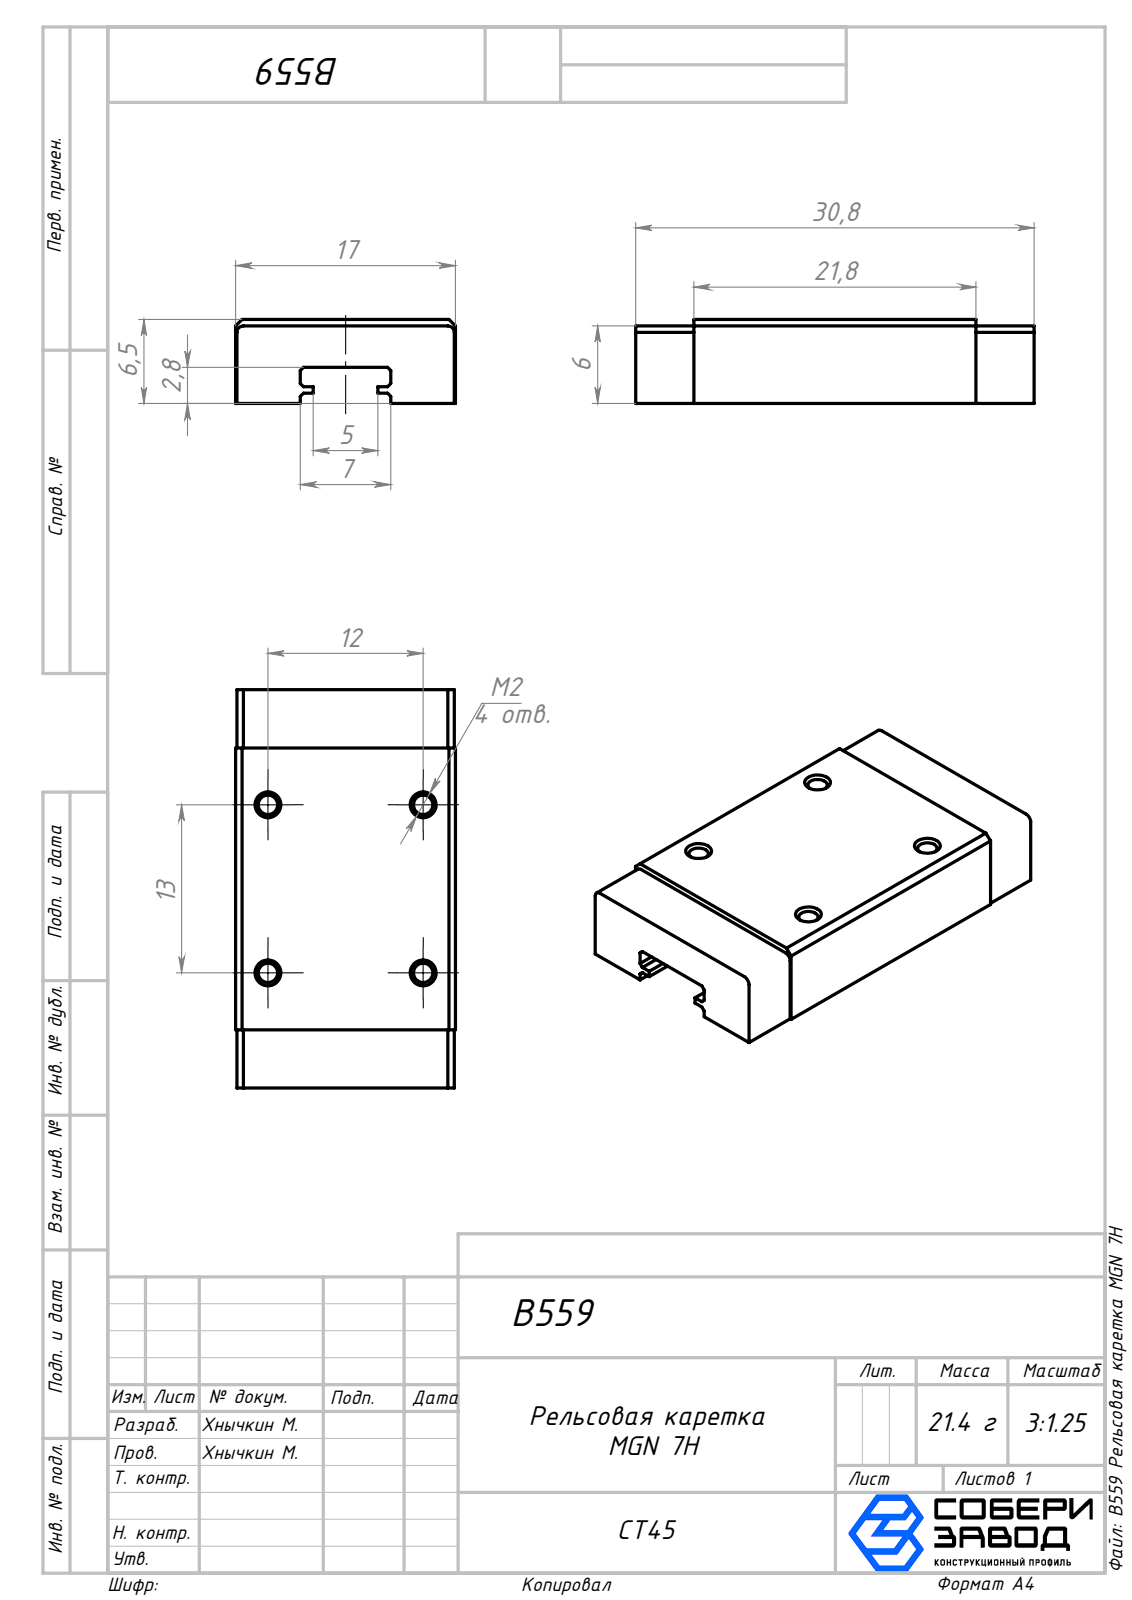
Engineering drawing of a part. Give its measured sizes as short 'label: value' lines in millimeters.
name: B559 Рельсовая каретка MGN 7H
written by: SolidWorks 2026 (AUTOMOTIVE_DESIGN)
unit: mm
bodies: 1 solid, 58 faces (38 planar, 12 cylindrical, 8 other)
size: 30.8 × 17 × 6.5
volume: 2 724 mm³; area: 1 915 mm²
holes: 4× ⌀1.5
rounds: 2× R0.5
face distances: 6.5, 6, 2.8, 3.7, 0.5, 3.2, 17, 5, 16.9, 12
hole spacings: 12, 13, 17.69
